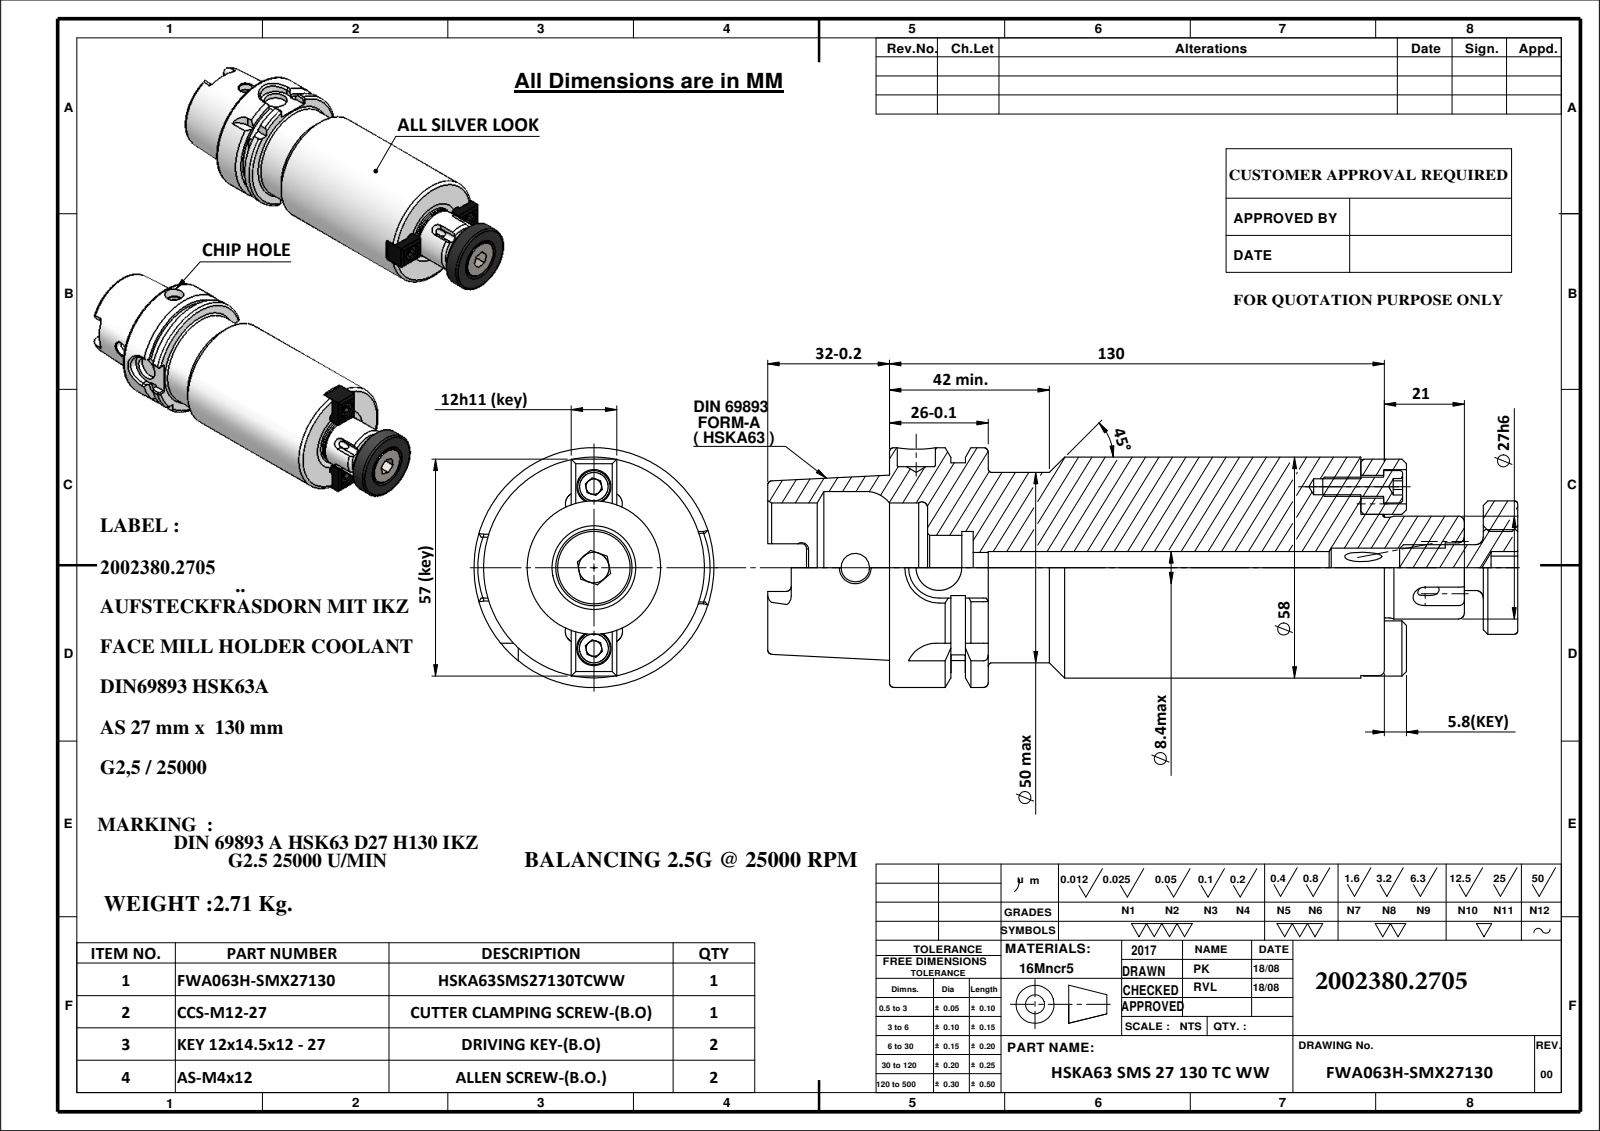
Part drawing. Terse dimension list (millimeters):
name: HSKA63SMS27130TCWW; AS-M5X16_AS-M5X12; 9163A-AS527130; CCS-M12-27 (+3 more)
written by: SolidWorks 2009 (CONFIG_CONTROL_DESIGN)
unit: mm
bodies: 7 solids, 382 faces (148 planar, 105 cylindrical, 129 other)
size: 197 × 63 × 63
volume: 357 959 mm³; area: 56 459 mm²
holes: 4× ⌀3, 2× ⌀4.2, 2× ⌀6, 2× ⌀9, 1× ⌀7.5, 1× ⌀8, 1× ⌀8.4, 1× ⌀10, 1× ⌀10.2, 1× ⌀12, 1× ⌀13, 1× ⌀17
bosses: 2× ⌀8.5, 2× ⌀5, 1× ⌀63, 1× ⌀58, 1× ⌀55, 1× ⌀50, 1× ⌀35, 1× ⌀27
rounds: 6× R1.3, 4× R2, 4× R2.88, 4× R3, 2× R8, 1× R9
face distances: 130, 12, 165, 35, 25.95, 104.05, 139.05, 113.8, 6.2, 123.8
hole spacings: 21.25, 22, 42.5
